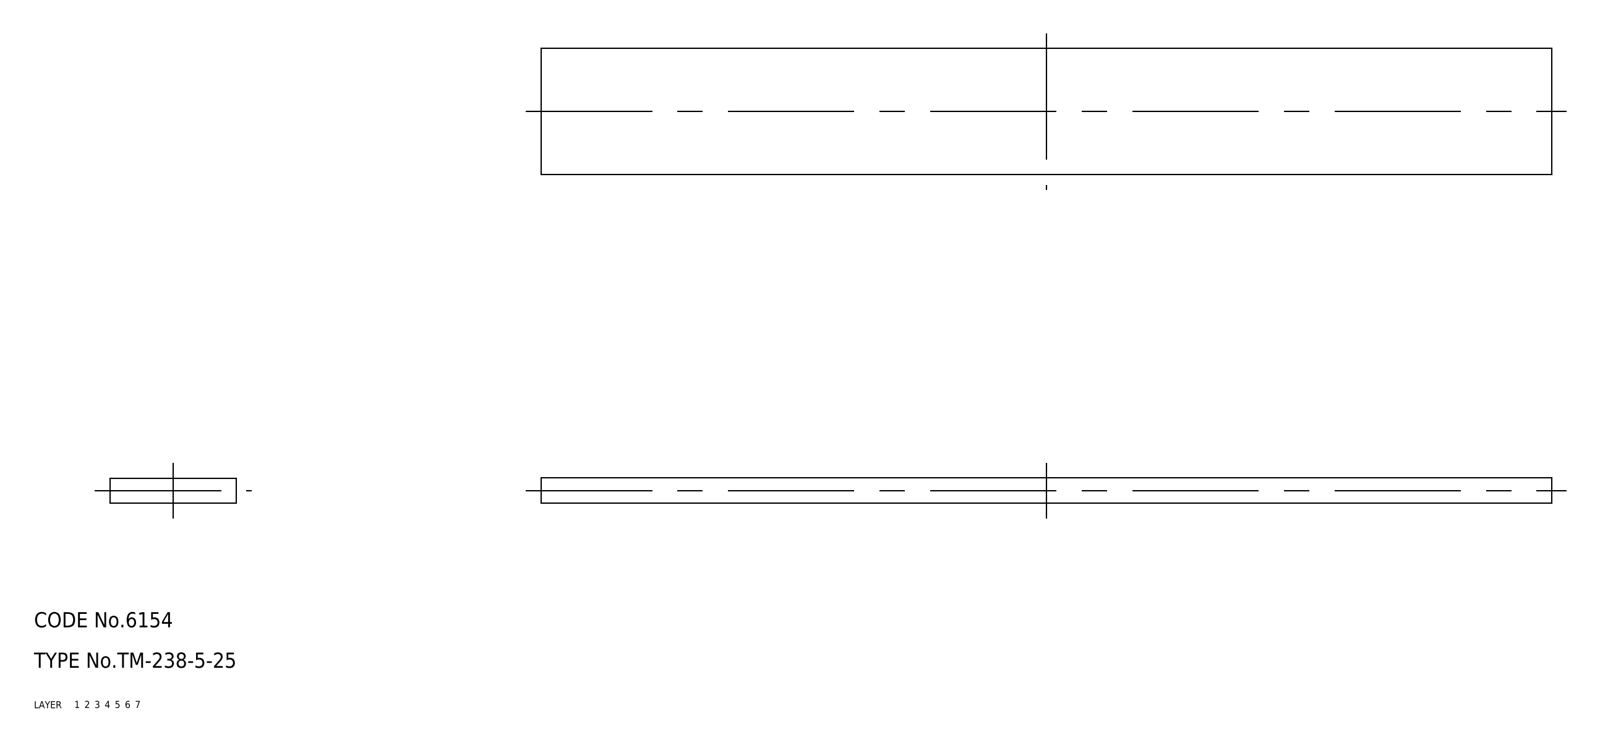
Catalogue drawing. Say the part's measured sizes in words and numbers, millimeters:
The part is named "rubber foam". Its 3-D file was written by "CADfix (AUTOMOTIVE_DESIGN)". It is 1 solid with 6 faces: 0 planar, 0 cylindrical and 6 other. Overall it measures 200 by 25 by 5 millimeters. Its volume is 25 000 cubic millimeters and its surface area 12 250 square millimeters.
